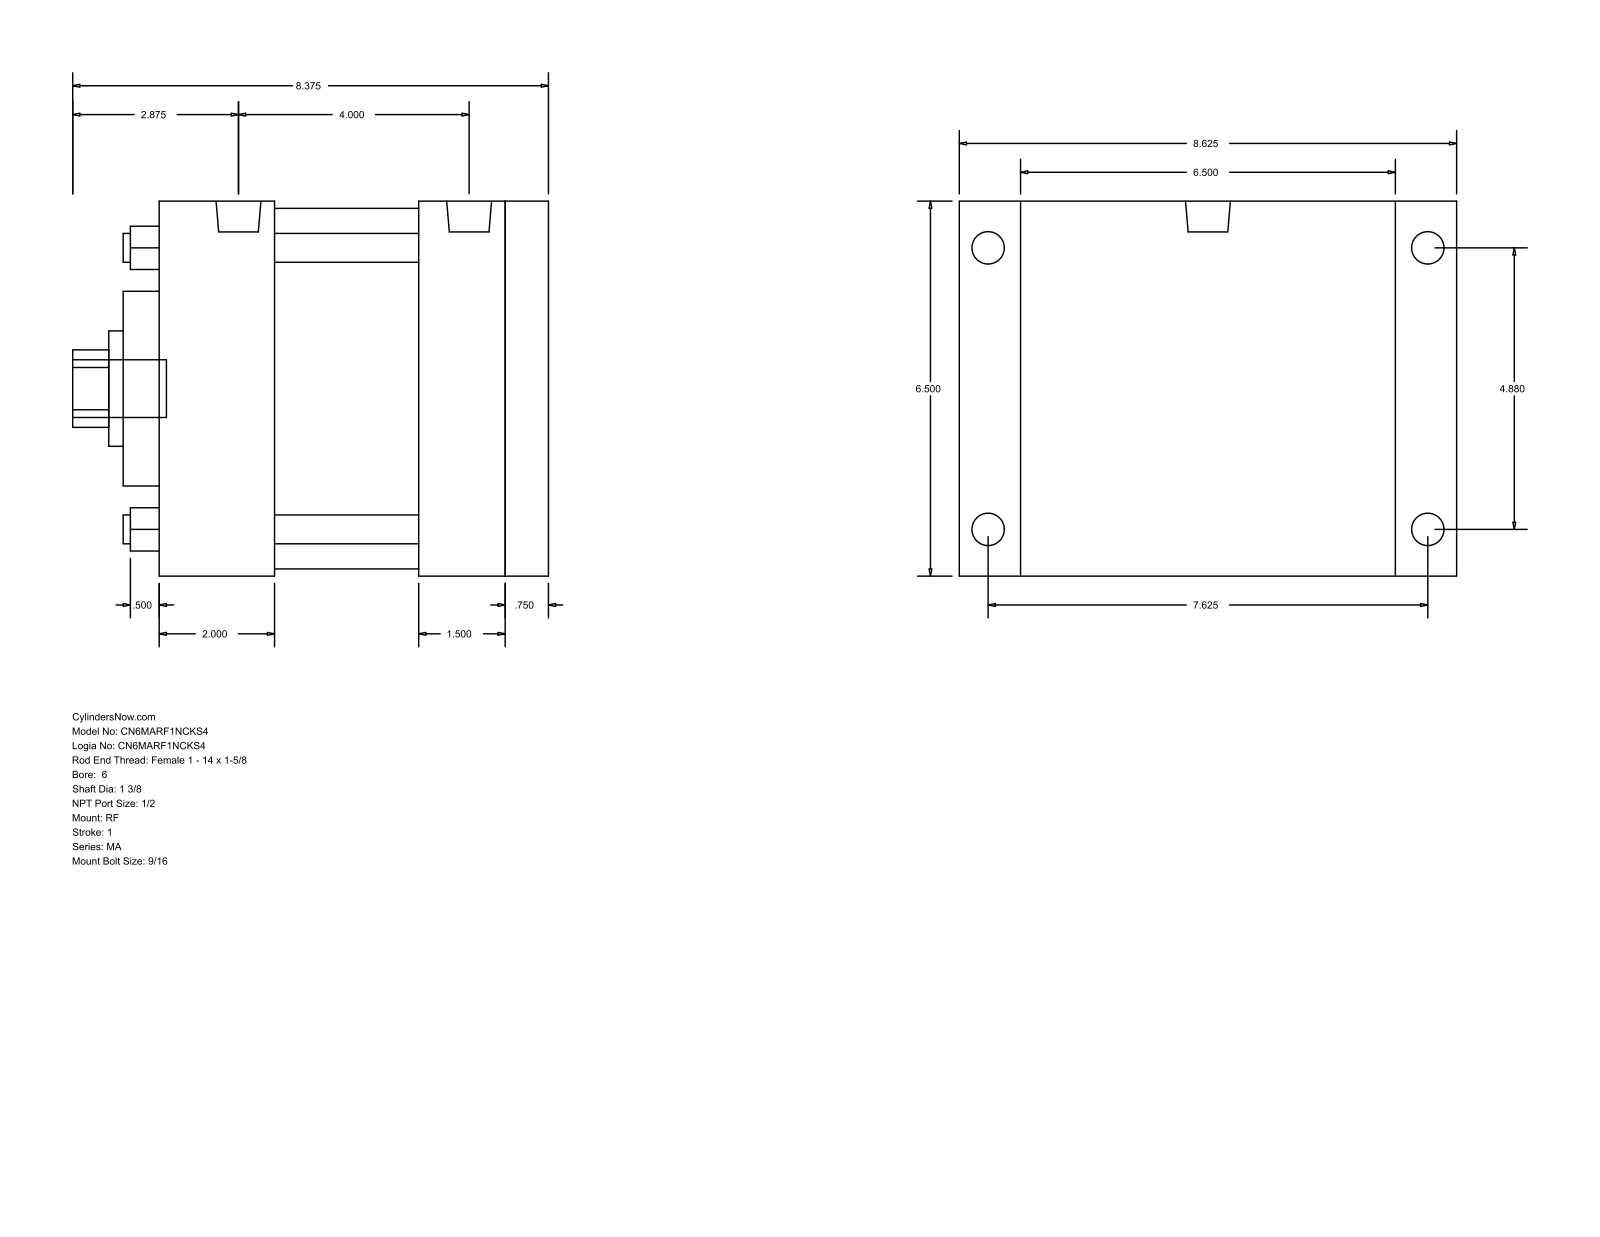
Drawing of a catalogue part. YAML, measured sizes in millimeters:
part_name: "MA_RF__0600_1.375"
step_written_by: "GSSL Pune (CONFIG_CONTROL_DESIGN)"
units: millimeters
bodies: {solids: 0, faces: 94, planar: 65, cylindrical: 29, other: 0}
overall_size: [219.07, 212.72, 165.1]
round_holes:
  - {diameter: 12.7, count: 4}
  - {diameter: 34.92, count: 1}
  - {diameter: 50.8, count: 1}
  - {diameter: 85.72, count: 1}
  - {diameter: 158.75, count: 1}
round_bosses_or_shafts:
  - {diameter: 17.46, count: 4}
  - {diameter: 14.29, count: 4}
  - {diameter: 19.77, count: 2}
  - {diameter: 25.4, count: 1}
partial_cylinders:
  - {radius: 17.06, count: 1}
face_to_face_distances: [165.1, 174.62, 66.67, 19.04, 155.58, 50.8, 104.78, 123.82, 117.47, 38.11]
hole_center_spacings: [87.65, 123.96, 175.31]
